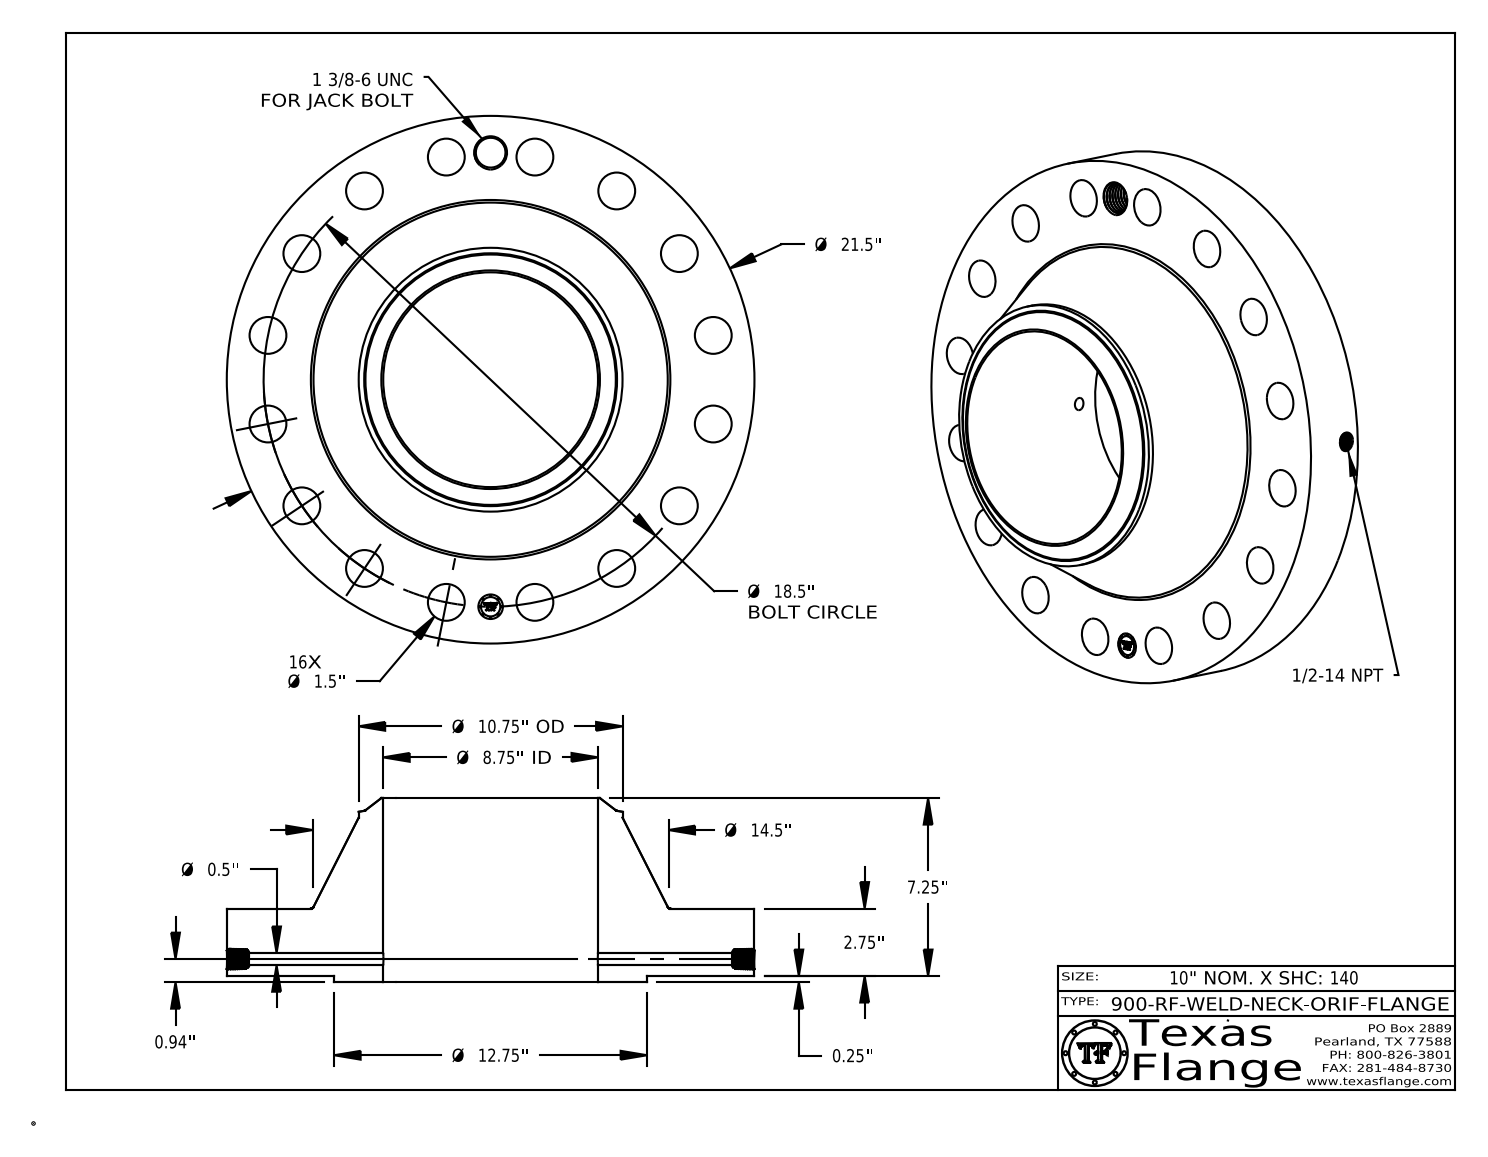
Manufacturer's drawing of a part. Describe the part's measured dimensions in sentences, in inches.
The part is named "900-RF-WELD-NECK". Its 3-D file was written by "CATIA V5 STEP AP214 (AUTOMOTIVE_DESIGN)". It is 1 solid with 798 faces: 369 planar, 113 cylindrical and 316 other. Overall it measures 21.5 by 21.5 by 7.5 inches. Its volume is 1 025 cubic inches and its surface area 1 298 square inches. Round holes: 16 of diameter 1.5, 1 of diameter 0.5, 1 of diameter 0.672, 1 of diameter 1, 1 of diameter 1.219, 1 of diameter 8.75. Round bosses or shafts: 8 of diameter 0.061, 1 of diameter 21.5, 1 of diameter 12.75, 1 of diameter 10.75, 1 of diameter 0.788. The main face-to-face distances are 2.75, 0.25, 3, 7.5, 7.25, 4.5, 2.985, 2.735, 0.015, 4.515. The hole center spacings are 10.278, 17.092, 3.609, 9.25, 7.08, 7.08, 9.25, 13.081.
